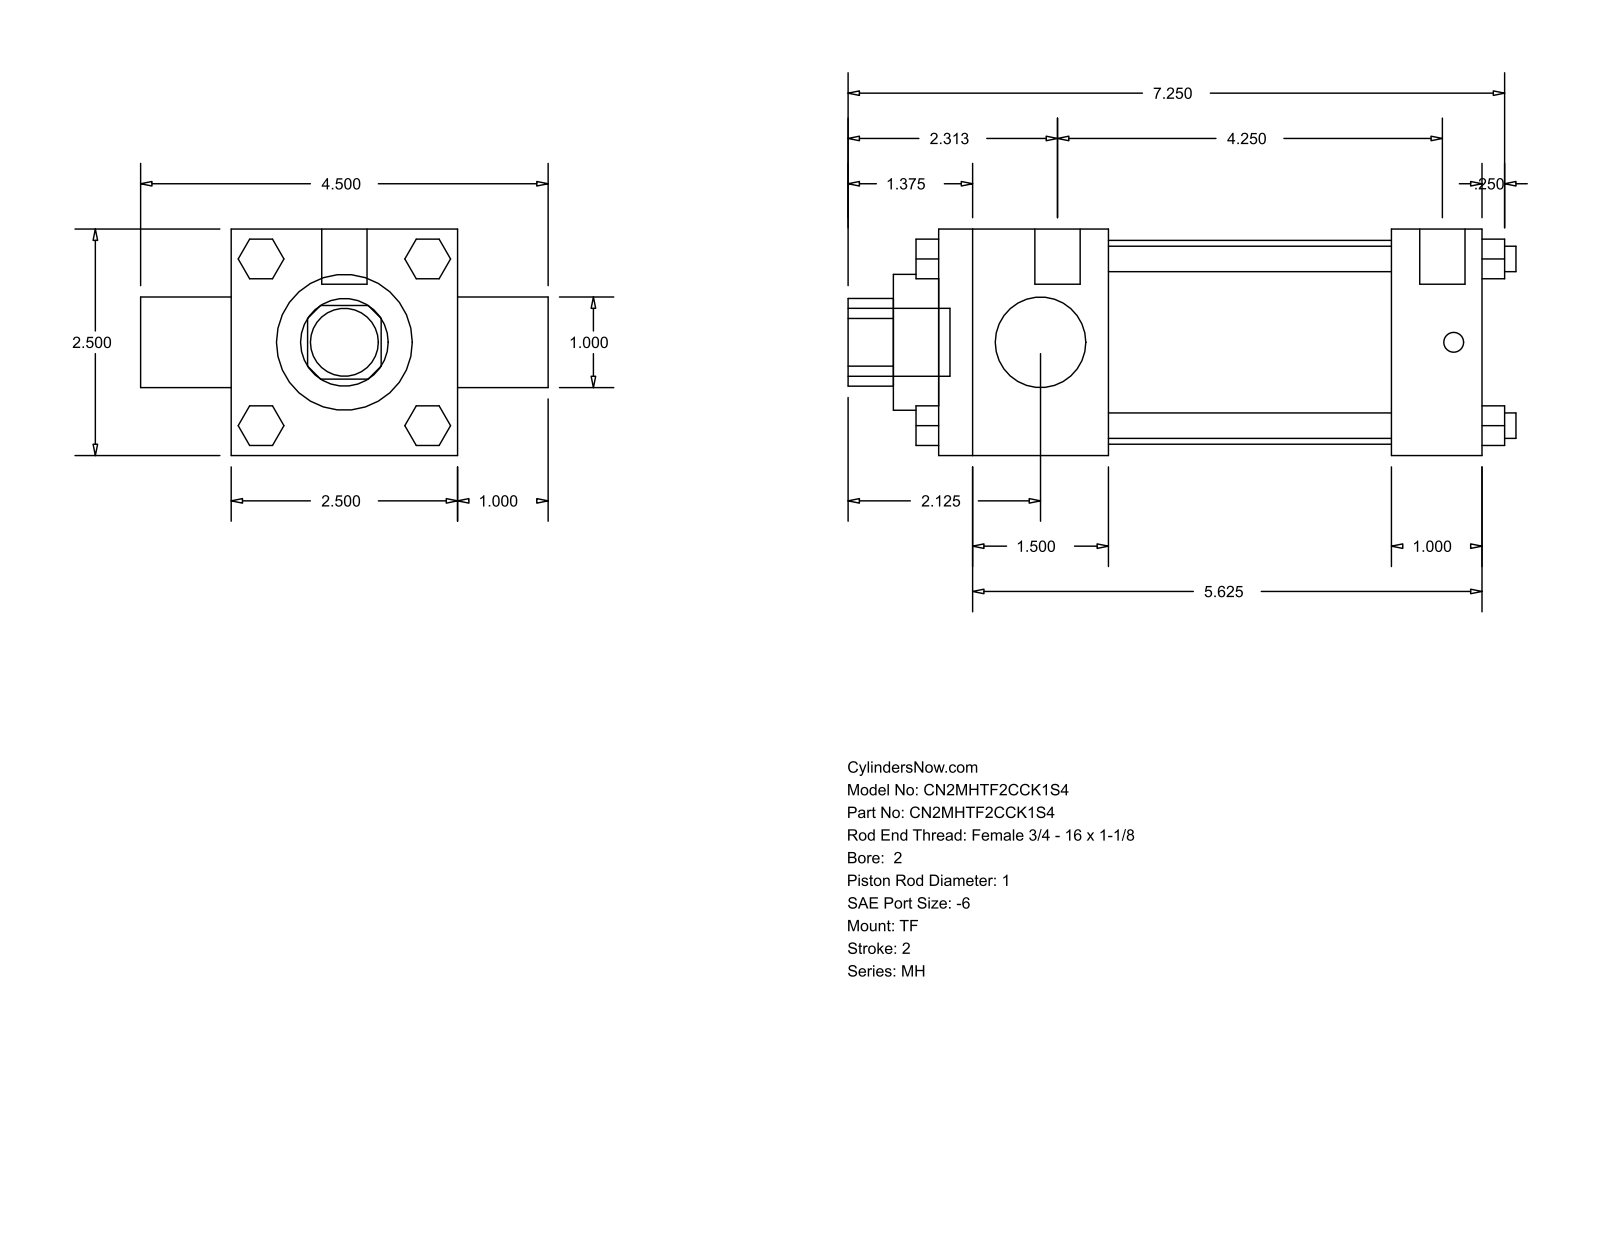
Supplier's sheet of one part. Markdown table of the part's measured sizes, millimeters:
| quantity | value |
| --- | --- |
| part name | MH_TF__0200_1 |
| STEP written by | GSSL Pune (CONFIG_CONTROL_DESIGN) |
| units | millimeters |
| bodies | 0 solids, 120 faces (92 planar, 28 cylindrical, 0 other) |
| overall size | 187.32 × 114.3 × 63.5 |
| round holes (diameter × count) | 25.4 × 2, 38.1 × 1, 57.15 × 1 |
| round bosses / shafts (diameter × count) | 7.14 × 4, 5.56 × 3, 12.7 × 2, 19.05 × 1 |
| partial cylindrical surfaces (radius × count) | 12.29 × 1 |
| main face-to-face distances | 63.5, 152.4, 25.4, 47.63, 127, 79.37, 104.77, 88.9, 165.1, 6.35 |
